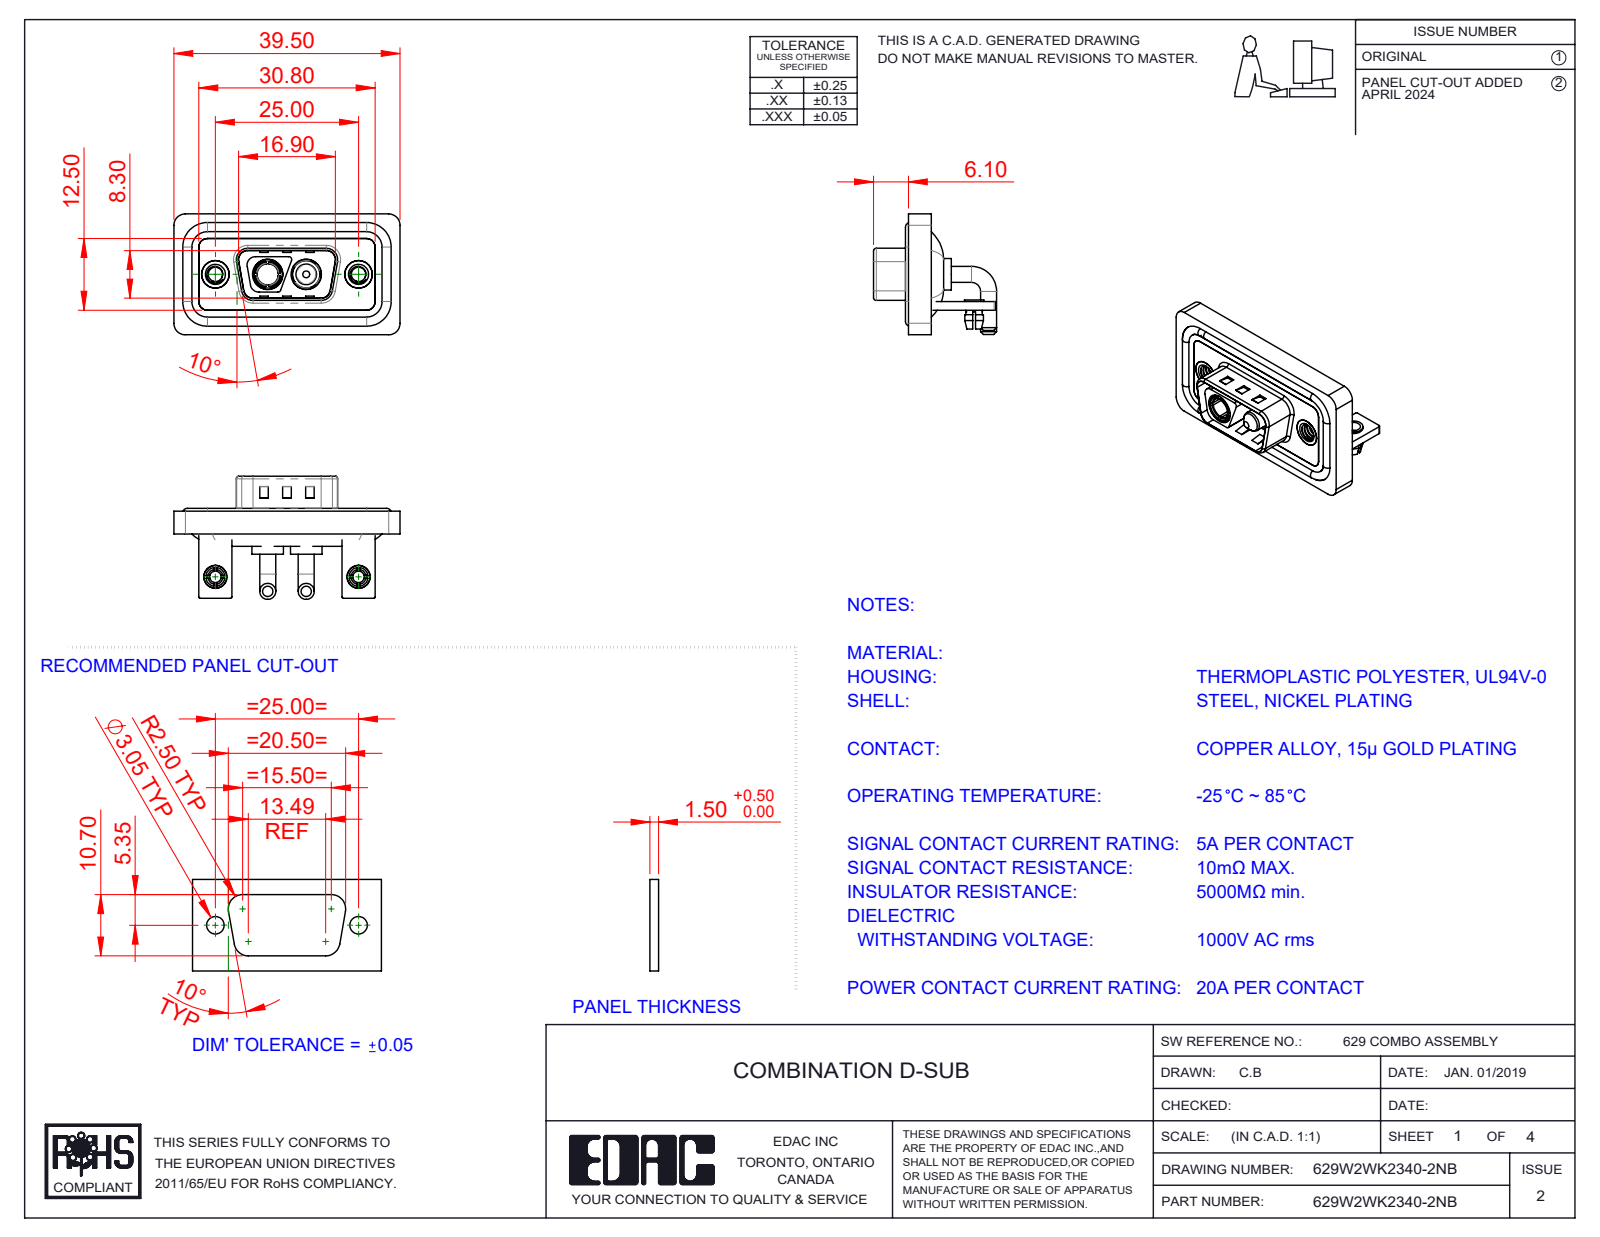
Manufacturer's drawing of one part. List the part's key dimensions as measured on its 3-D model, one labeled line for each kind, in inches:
Part name (STEP PRODUCT): Power Pin_20A RA; 629Combo Stabilizer Bracket; 629Combo Shell Front_09 Contacts; 629W2WK2340-2NB (+6 more)
STEP written by: SolidWorks 2023 (CONFIG_CONTROL_DESIGN)
Units: inches
Bodies: 15 solids, 672 faces (257 planar, 281 cylindrical, 134 other)
Overall size (bounding box): 1.555 × 0.846 × 0.831
Volume: 0.305 in³ · Surface area: 12.91 in²
Round holes (diameter × count): ⌀0.098 ×4, ⌀0.079 ×2, ⌀0.126 ×2, ⌀0.157 ×2, ⌀0.189 ×2, ⌀0.191 ×2, ⌀0.197 ×2, ⌀0.209 ×2, ⌀0.146 ×1
Round bosses / shafts (diameter × count): ⌀0.11 ×4, ⌀0.063 ×4, ⌀0.217 ×2, ⌀0.205 ×2, ⌀0.193 ×2, ⌀0.187 ×2, ⌀0.157 ×2, ⌀0.148 ×2
Partial cylindrical surfaces — rounded edges, fillets, slot ends (radius × count): R0.059 ×20, R0.079 ×19, R0.01 ×16, R0.02 ×11, R0.063 ×8, R0.024 ×4, R0.026 ×4, R0.035 ×4
Main face-to-face distances: 0.016, 0.059, 0.114, 0.031, 0.043, 0.047, 0.083, 0.063, 0.146, 0.098
Hole centre spacings: 0.36, 0.624, 0.984, 0.265
